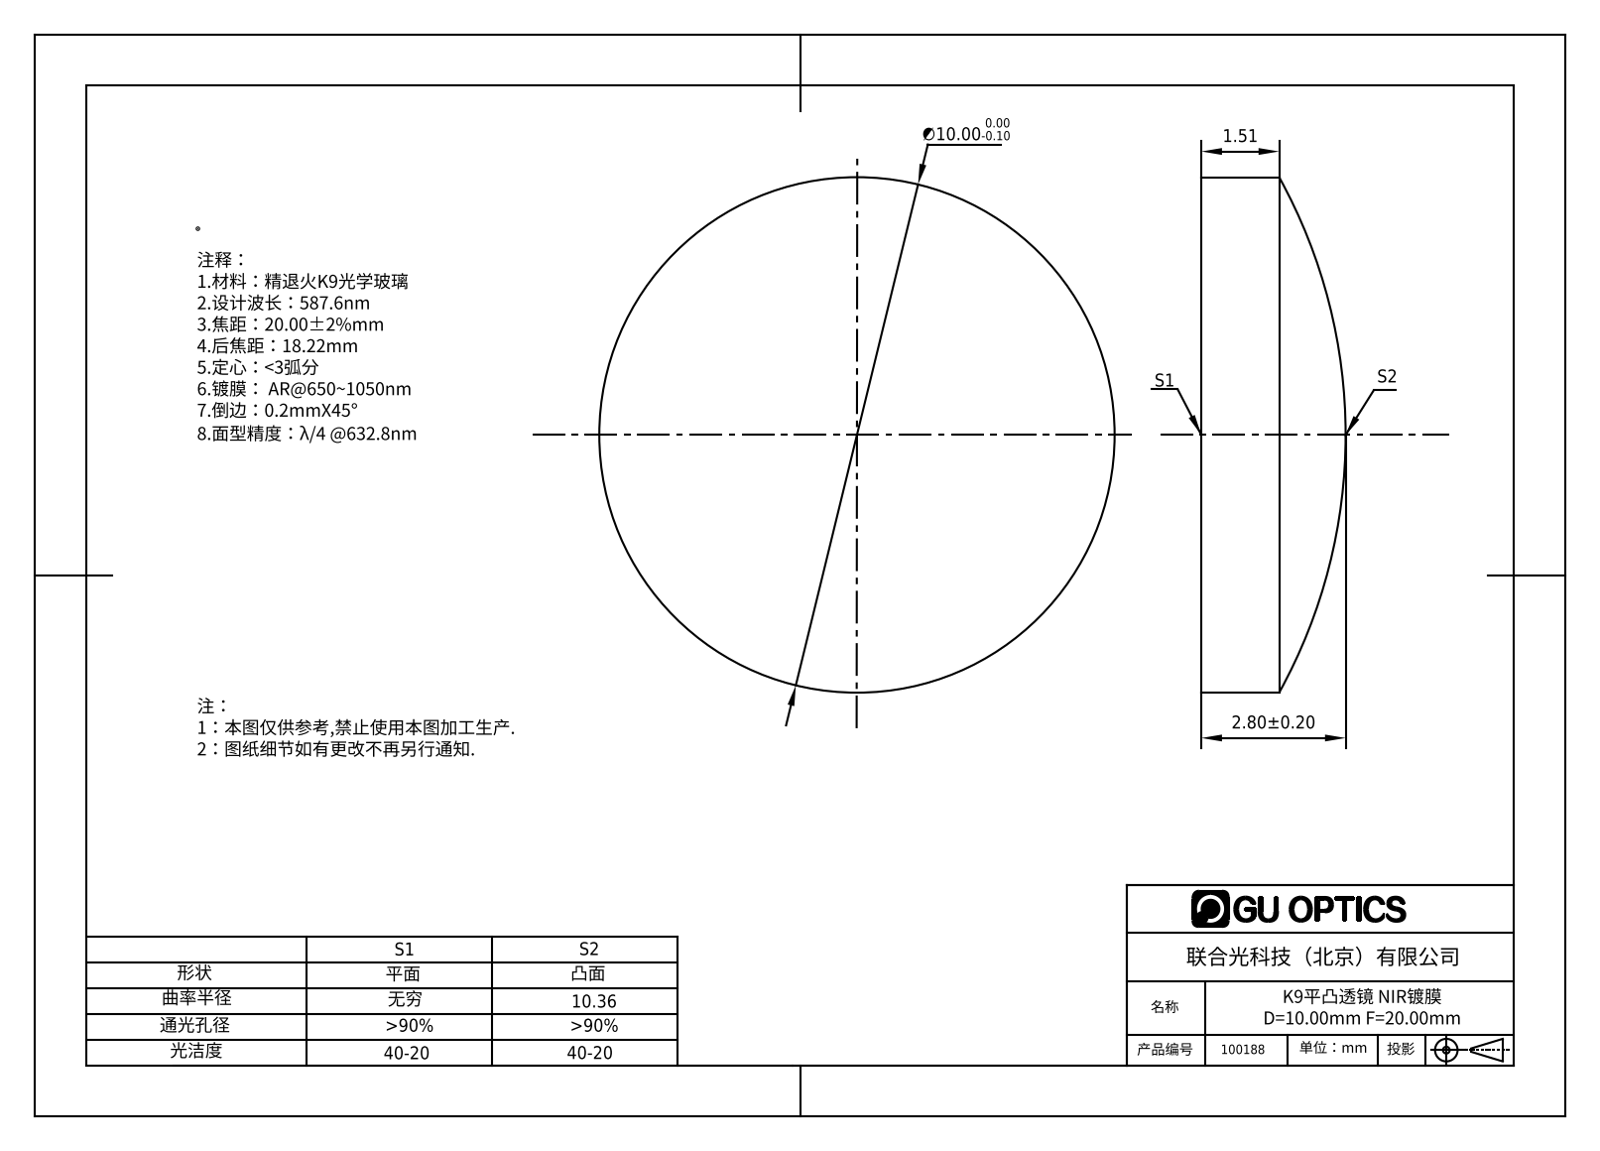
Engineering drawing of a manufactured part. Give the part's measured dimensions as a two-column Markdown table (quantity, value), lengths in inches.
| quantity | value |
| --- | --- |
| part name | 100188 |
| STEP written by | SolidWorks 2016 (AUTOMOTIVE_DESIGN) |
| units | inches |
| bodies | 1 solid, 5 faces (1 planar, 2 cylindrical, 2 other) |
| overall size | 0.394 × 0.394 × 0.11 |
| volume | 0.01 in³ |
| surface area | 0.326 in² |
| round bosses / shafts (diameter × count) | 0.394 × 1 |
